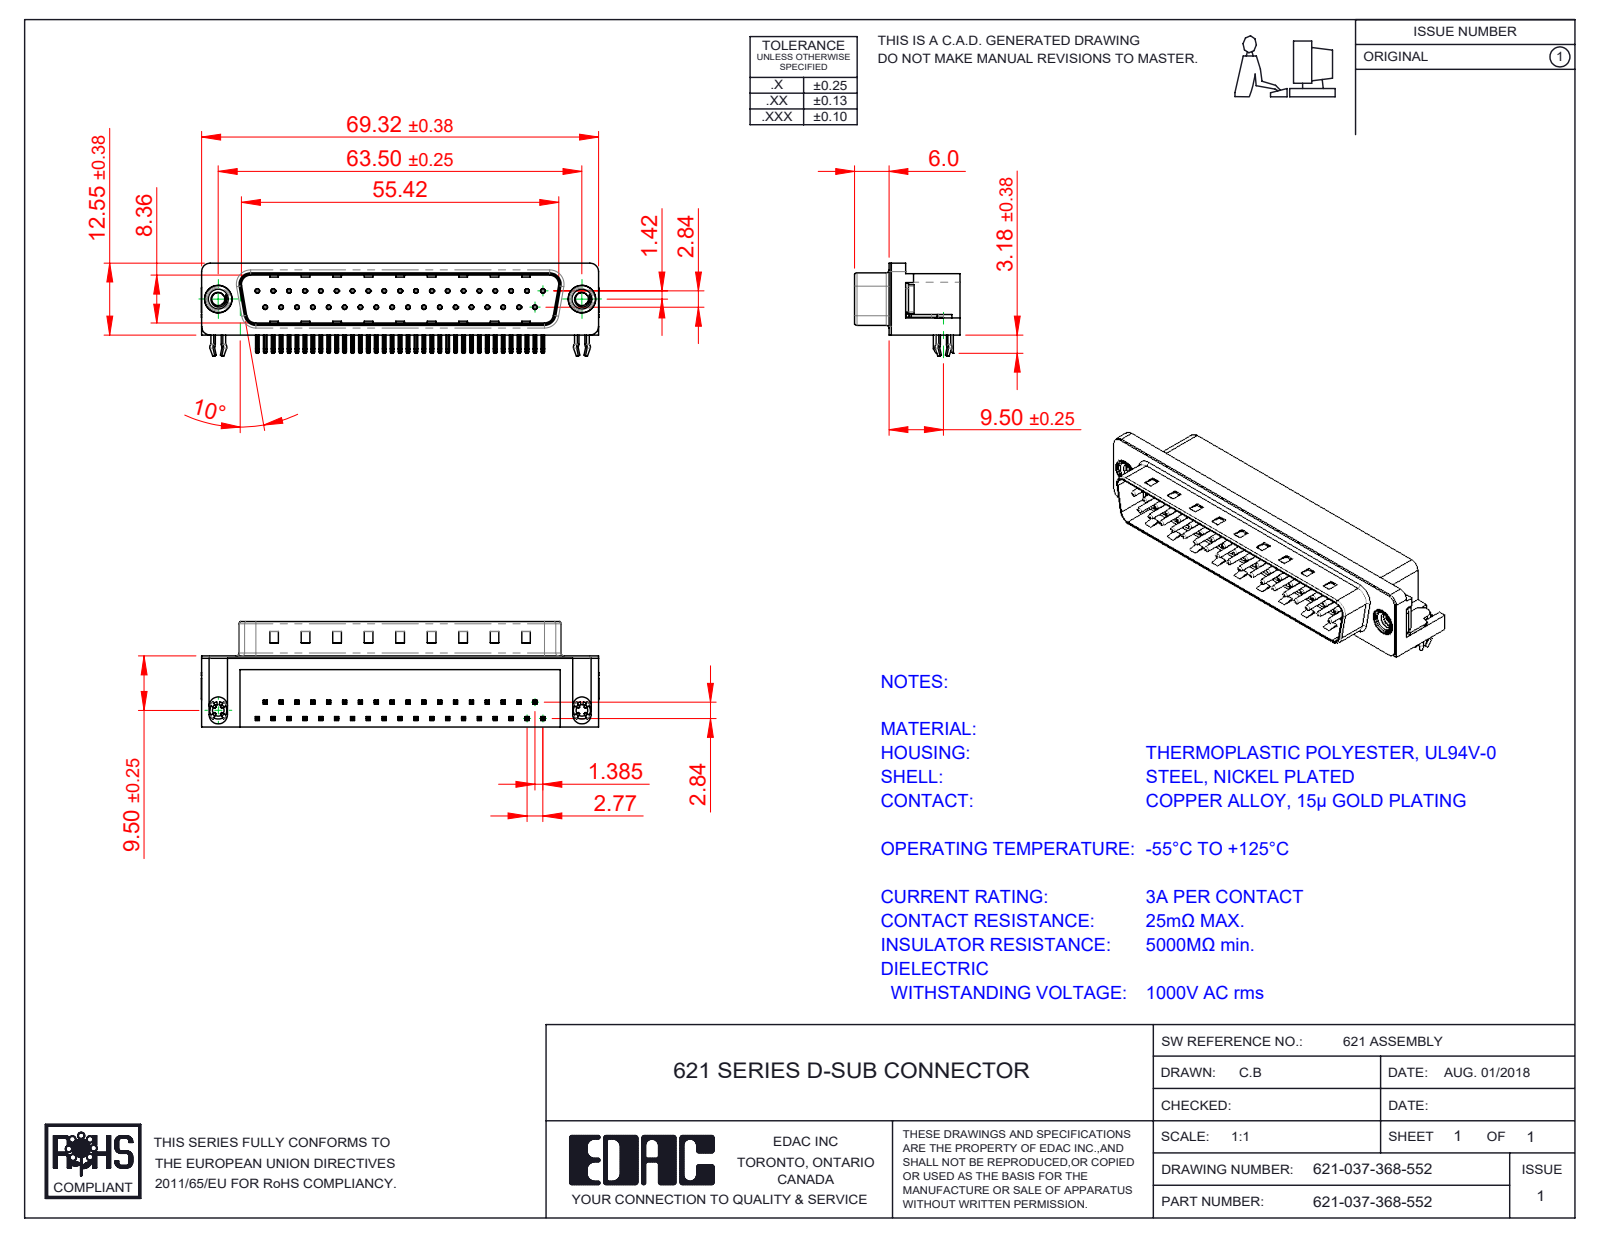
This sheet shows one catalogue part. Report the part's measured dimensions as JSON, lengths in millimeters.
{"part_name": "621 4-40 Threaded Rivet; 621 Housing_37 Socket; 621 Contact Bottom; 621 Shell_37 Socket (+3 more)", "step_written_by": "SolidWorks 2016 (CONFIG_CONTROL_DESIGN)", "units": "millimeters", "bodies": {"solids": 43, "faces": 3229, "planar": 2013, "cylindrical": 927, "other": 289}, "overall_size": [69.4, 18.4, 15.73], "volume_mm3": 8634, "surface_area_mm2": 10174, "round_holes": [[0.35, 37], [0.8, 37], [2.26, 4], [4, 2], [4.8, 2], [5, 2]], "round_bosses_or_shafts": [[0.75, 37], [4.9, 2], [4.75, 2], [3.9, 2], [3.26, 2]], "partial_cylinders_radius": [[0.25, 156], [0.12, 74], [1, 16], [0.5, 9], [1.6, 8], [1.5, 7], [0.9, 4], [2, 4]], "face_to_face_distances": [0.4, 12, 10.35, 8.76, 2.1, 1.7, 10.46, 10.86, 9, 12.4], "hole_center_spacings": [3.16, 2.77, 5.54, 8.31, 11.08, 13.85, 19.39, 22.16]}
